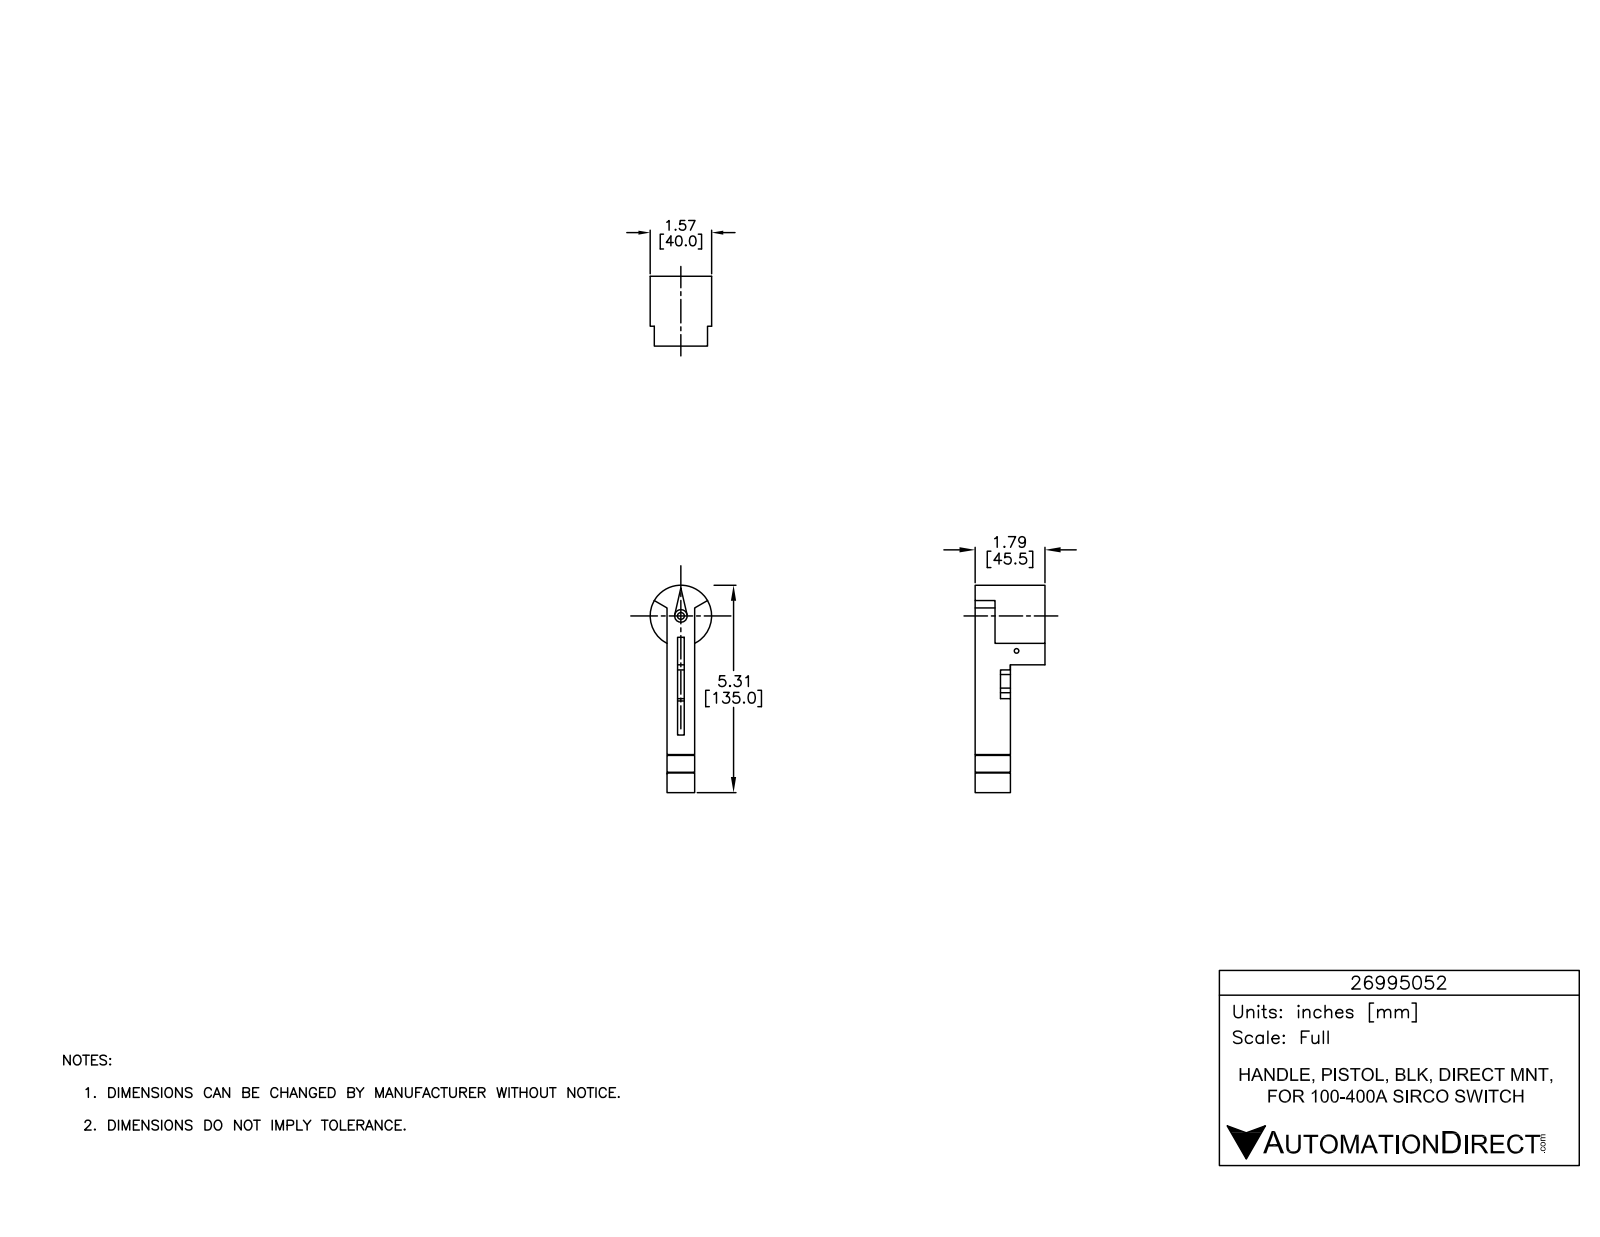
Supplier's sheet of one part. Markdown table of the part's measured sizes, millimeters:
| quantity | value |
| --- | --- |
| part name | 26995052 |
| STEP written by | SolidWorks 2015 (AUTOMOTIVE_DESIGN) |
| units | millimeters |
| bodies | 1 solid, 124 faces (109 planar, 15 cylindrical, 0 other) |
| overall size | 135 × 45.5 × 40 |
| volume | 77 580 mm³ |
| surface area | 25 170 mm² |
| round holes (diameter × count) | 3 × 1, 4.5 × 1, 6 × 1, 8.2 × 1 |
| round bosses / shafts (diameter × count) | 40 × 1 |
| main face-to-face distances | 18, 11.2, 6.8, 23, 4.4, 22.5, 45.5, 10, 1.4, 16.6 |
| hole center spacings | 15 |
